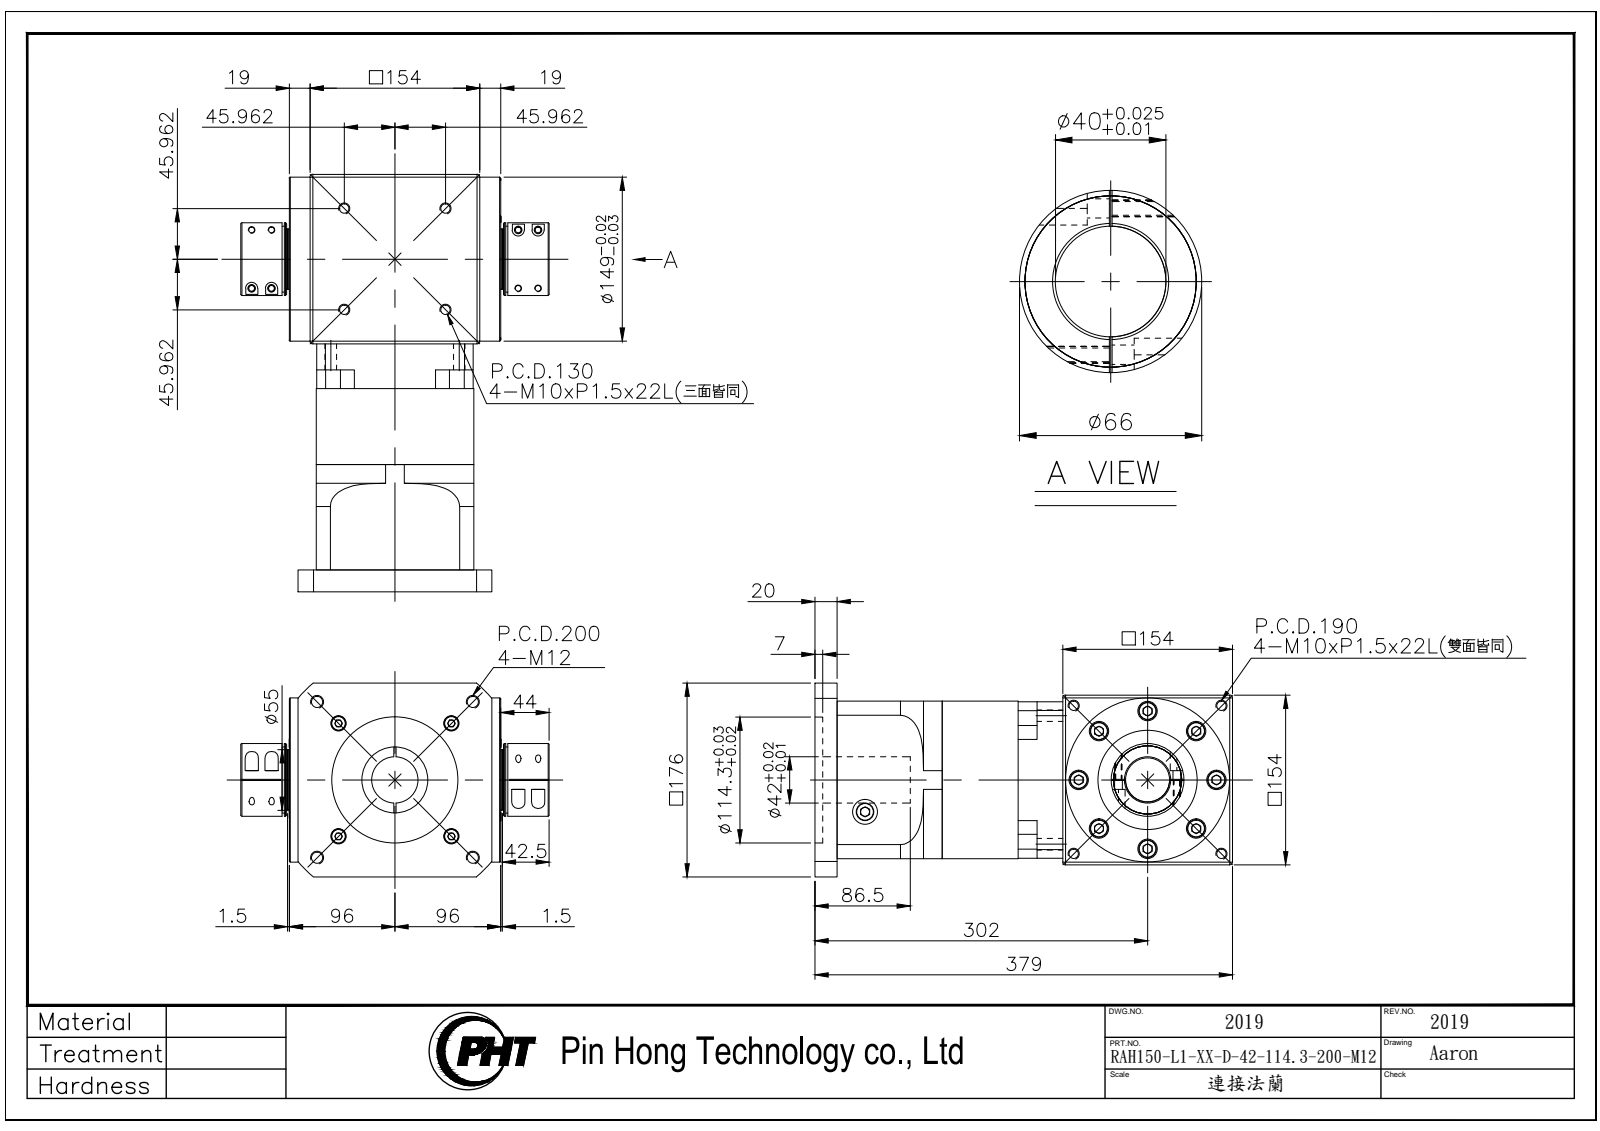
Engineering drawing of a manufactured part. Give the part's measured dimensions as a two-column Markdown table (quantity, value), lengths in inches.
| quantity | value |
| --- | --- |
| part name | RAH150-L1-XX-D-42-114.3-200-M12_2019 |
| STEP written by | SolidWorks 2016 (AUTOMOTIVE_DESIGN) |
| units | inches |
| bodies | 2 solids, 1360 faces (688 planar, 438 cylindrical, 234 other) |
| overall size | 14.921 × 11.024 × 6.929 |
| volume | 489.2 in³ |
| surface area | 881.3 in² |
| round holes (diameter × count) | 0.335 × 12, 0.354 × 12, 0.551 × 12, 0.433 × 8, 0.689 × 8, 0.276 × 6, 0.268 × 4, 0.402 × 4, 0.413 × 4, 0.886 × 2, 1.575 × 1, 1.654 × 1 |
| round bosses / shafts (diameter × count) | 0.63 × 12, 0.512 × 12, 0.413 × 8, 0.394 × 8, 0.236 × 8, 5.866 × 1, 5.669 × 1, 5.63 × 1 |
| partial cylindrical surfaces (radius × count) | 0.139 × 8, 0.217 × 8, 0.394 × 4, 3.15 × 1, 3.642 × 1, 3.74 × 1, 4.228 × 1, 4.528 × 1 |
| main face-to-face distances | 6.063, 0.217, 5.846, 5.63, 8.858, 14.921, 0.965, 6.594, 0.157, 0.433 |
| hole center spacings | 2.598, 0.674, 0.756, 0.999, 1.578, 1.883, 2.651, 3.14 |
